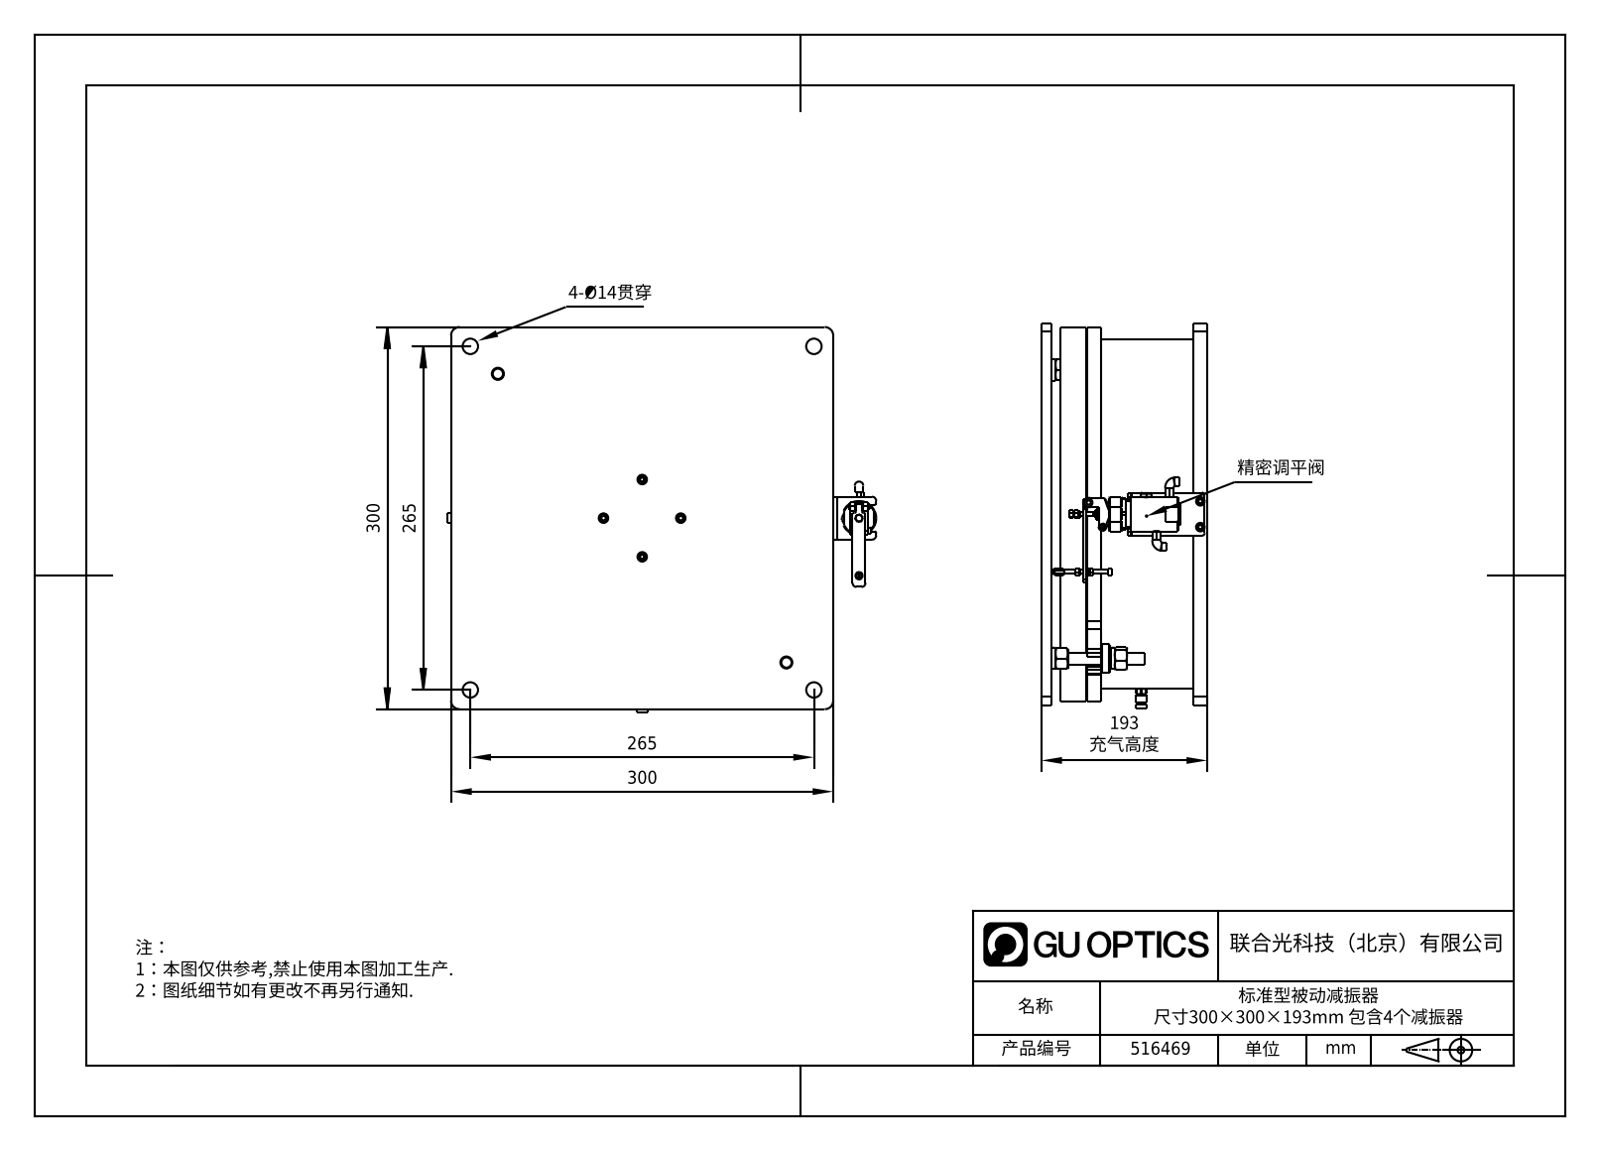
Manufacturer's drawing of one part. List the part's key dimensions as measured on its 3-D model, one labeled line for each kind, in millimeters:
Part name (STEP PRODUCT): 516469
STEP written by: SolidWorks 2020 (CONFIG_CONTROL_DESIGN)
Units: millimetres
Bodies: 0 solids, 480 faces (269 planar, 146 cylindrical, 65 other)
Overall size (bounding box): 350 × 300 × 193
Round holes (diameter × count): ⌀9.7 ×3, ⌀13 ×3, ⌀12.7 ×2, ⌀5 ×1, ⌀11.5 ×1, ⌀13.84 ×1, ⌀25.1 ×1, ⌀285 ×1
Round bosses / shafts (diameter × count): ⌀12 ×5, ⌀11 ×5, ⌀14 ×4, ⌀10 ×4, ⌀30 ×3, ⌀12.6 ×3, ⌀10.4 ×3, ⌀8.45 ×3
Partial cylindrical surfaces — rounded edges, fillets, slot ends (radius × count): R5 ×10, R10 ×10, R0.3 ×3, R2 ×3, R7 ×3, R3 ×2, R4.5 ×2, R0.74 ×1
Main face-to-face distances: 12, 181, 169, 193, 48, 133, 121, 60, 36, 10
Hole centre spacings: 138.88, 157.68, 20.93, 40, 130.86, 133, 156.84, 180
